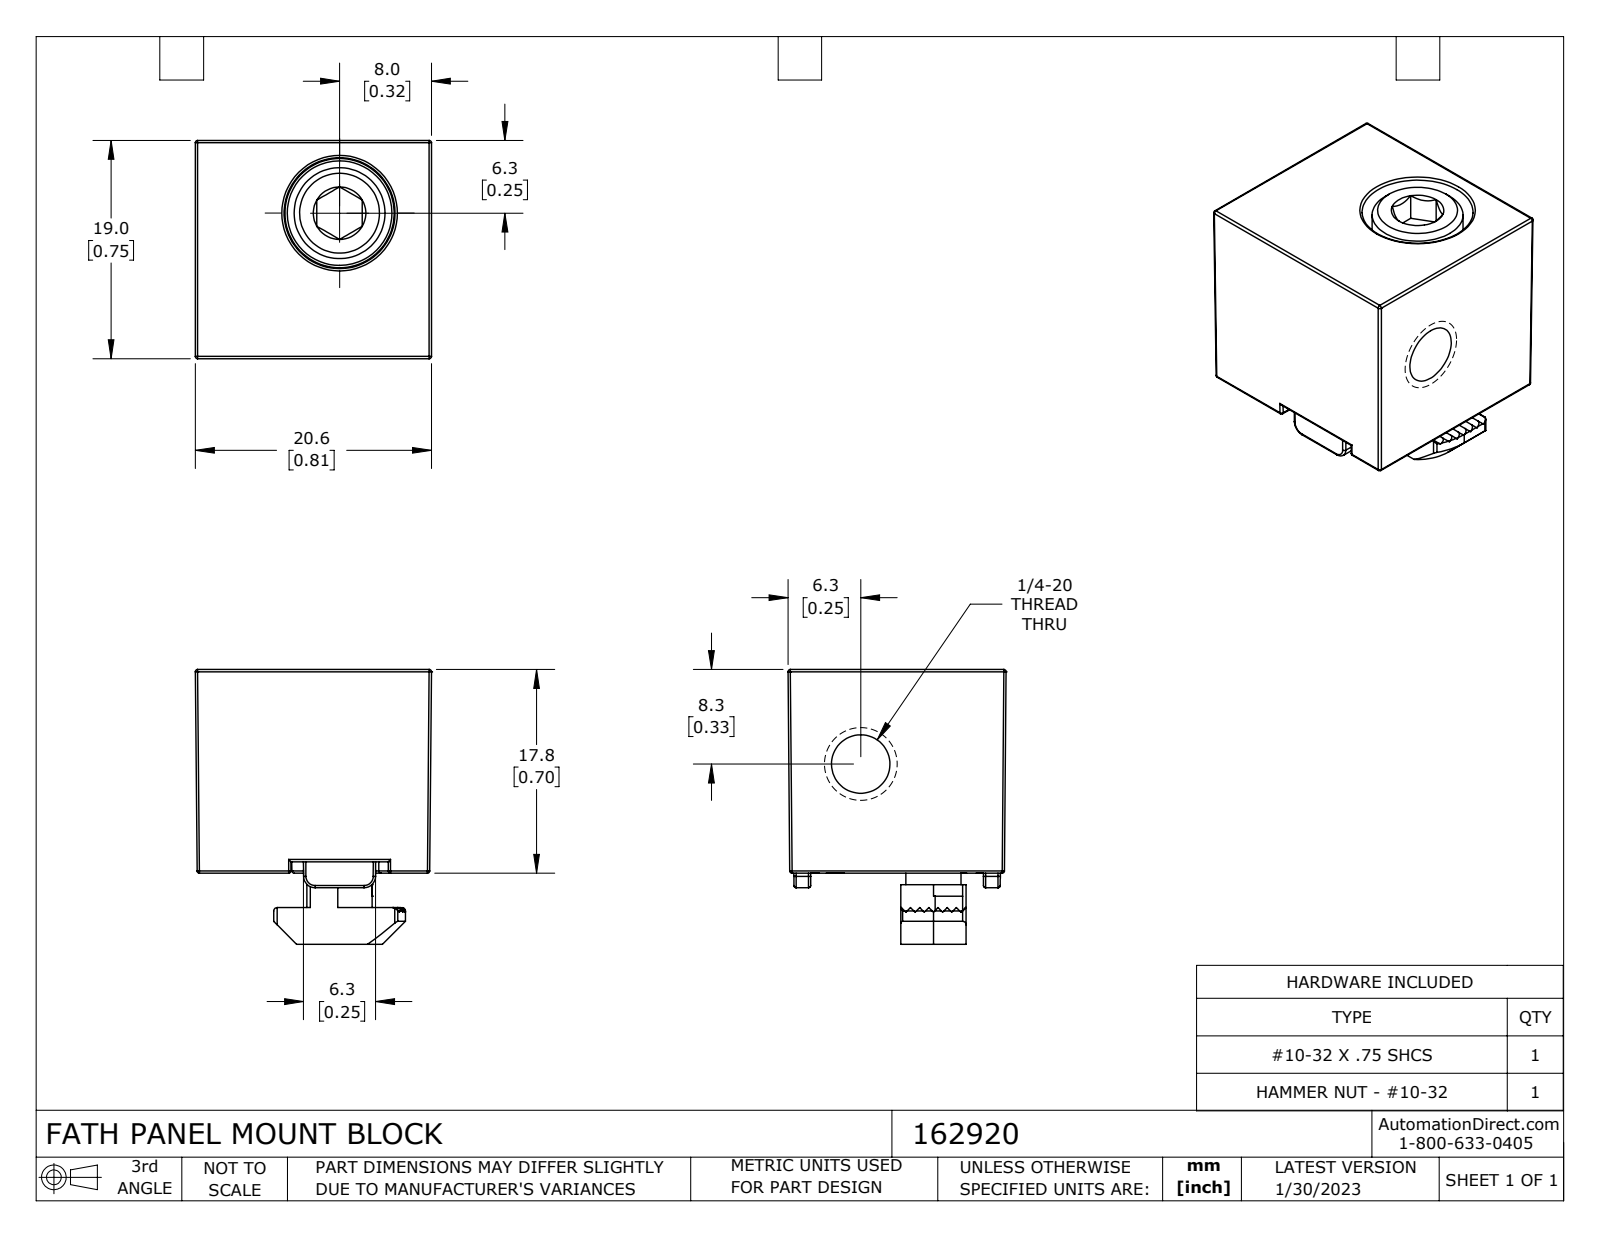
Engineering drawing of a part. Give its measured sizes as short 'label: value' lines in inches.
name: 162920
written by: SolidWorks 2021 (CONFIG_CONTROL_DESIGN)
unit: in
bodies: 2 solids, 253 faces (98 planar, 85 cylindrical, 70 other)
size: 0.944 × 0.812 × 0.75
volume: 0.346 in³; area: 6.446 in²
holes: 1× ⌀0.159, 1× ⌀0.201
bosses: 1× ⌀0.313, 1× ⌀0.19
rounds: 43× R0.008, 8× R0.012, 3× R0.083, 2× R0.039, 2× R0.118, 1× R0.179, 1× R0.226
face distances: 0.7, 0.401, 0.19, 0.58, 0.224, 0.079, 0.309, 0.039, 0.47, 0.244
